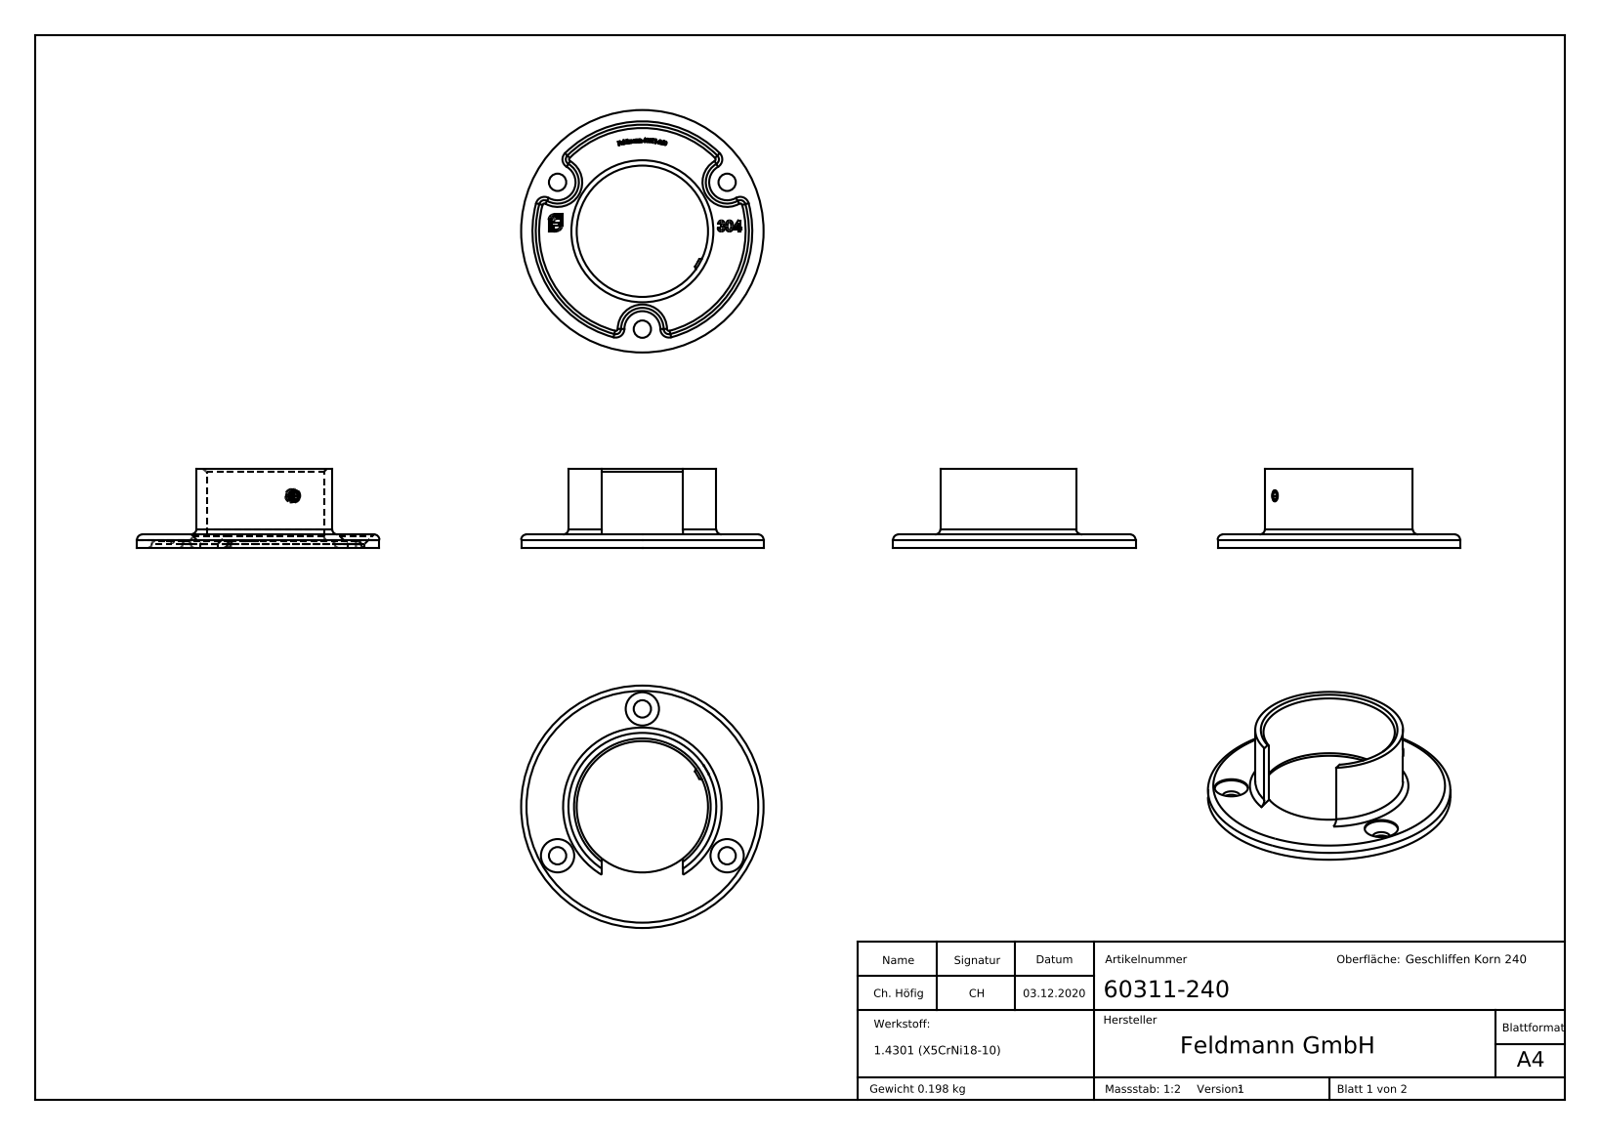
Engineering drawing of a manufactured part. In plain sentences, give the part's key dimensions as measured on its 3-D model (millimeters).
The part is named "60311-240; 60311-240 Teil1_60311-240 Teil1; 60311-240 Teil1; DIN913_DIN 913 M5x4 (+1 more)". Its 3-D file was written by "SolidWorks 2018 (CONFIG_CONTROL_DESIGN)". It is 2 solids with 394 faces: 182 planar, 22 cylindrical and 190 other. Overall it measures 91 by 91 by 29.5 millimeters. Its volume is 25 040 cubic millimeters and its surface area 17 711 square millimeters. Round holes: 3 of diameter 6.5, 3 of diameter 12.5, 1 of diameter 4.2, 1 of diameter 49.3. Round bosses or shafts: 1 of diameter 91, 1 of diameter 55.5, 1 of diameter 5. The main face-to-face distances are 2.5, 5, 29.5, 27, 24.5, 30.5, 2.6, 2.4, 26.9, 18.25. The hole center spacings are 36.75, 63.66, 36.76, 63.65.
